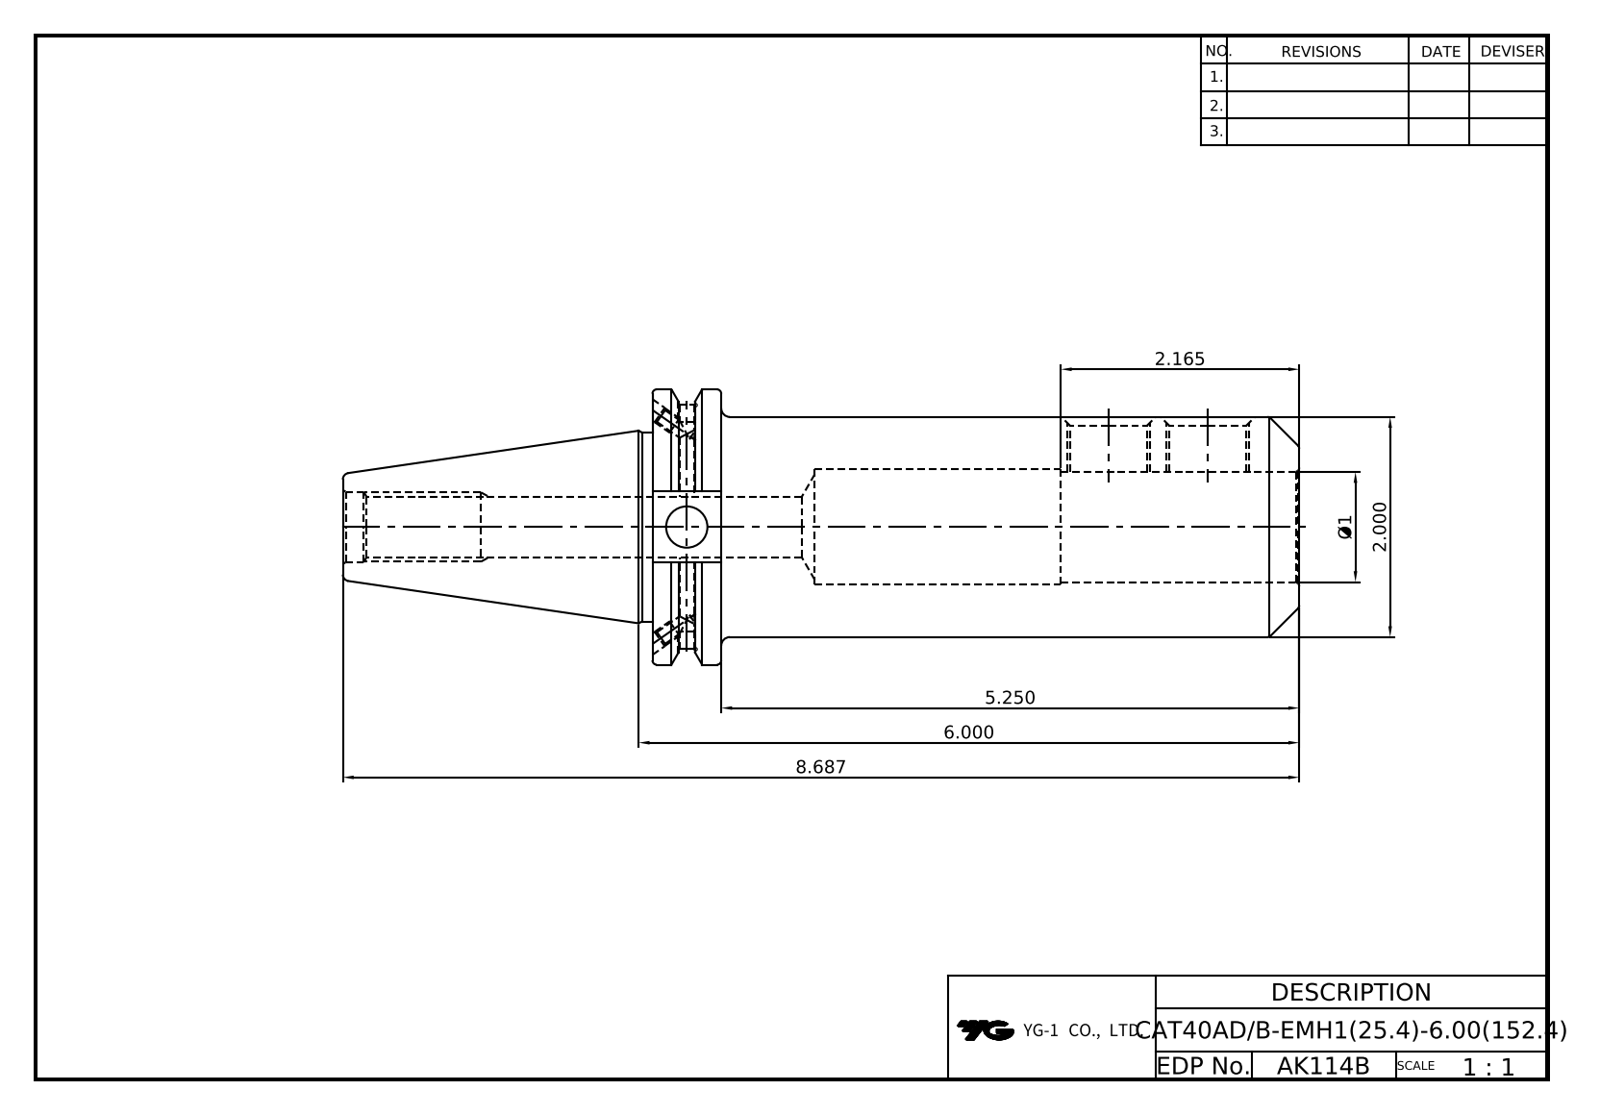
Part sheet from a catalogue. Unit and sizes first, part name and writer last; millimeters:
Units: millimetres
Overall size (bounding box): 220.65 × 63.5 × 61.09
Round holes (diameter × count): ⌀3.24 ×4, ⌀4 ×2, ⌀4.2 ×2, ⌀17.32 ×2, ⌀9.53 ×1, ⌀13.39 ×1, ⌀16.3 ×1, ⌀25.4 ×1, ⌀26.6 ×1
Round bosses / shafts (diameter × count): ⌀63.5 ×1, ⌀50.8 ×1, ⌀43.6 ×1
Partial cylindrical surfaces — rounded edges, fillets, slot ends (radius × count): R8.19 ×1, R28.15 ×1
Main face-to-face distances: 15.88, 149.23, 133.35, 37.47, 21.59, 111.76, 47.6, 16.38, 71.42, 87.3
Hole centre spacings: 22.9
Volume: 297 685 mm³ · Surface area: 51 971 mm²
Bodies: 1 solid, 93 faces (37 planar, 32 cylindrical, 24 other)
Part name (STEP PRODUCT): LO-CAT40ADB-EMH25.4-152.4
STEP written by: Autodesk Inventor 2025 (AUTOMOTIVE_DESIGN)
